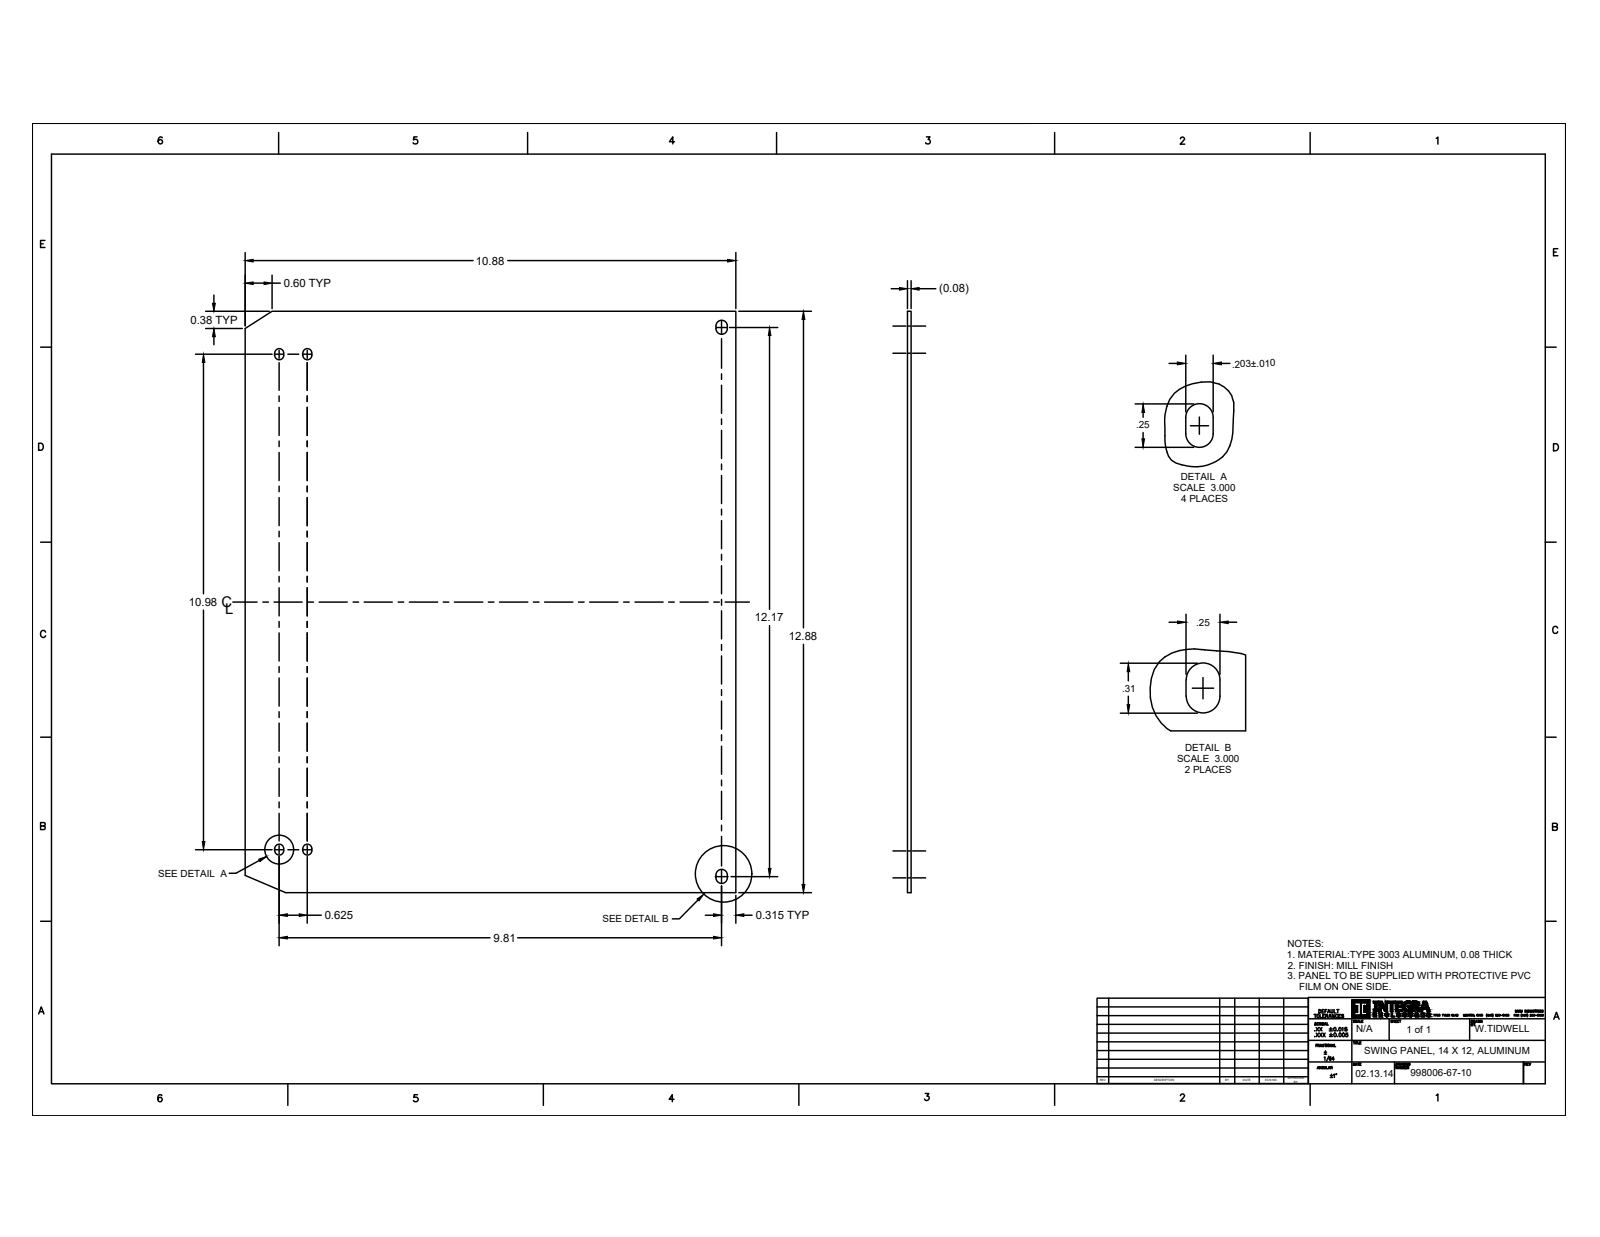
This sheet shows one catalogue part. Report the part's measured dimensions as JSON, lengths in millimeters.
{"part_name": "998006-67-10", "step_written_by": "CREO PARAMETRIC BY PTC INC, 2018050 (CONFIG_CONTROL_DESIGN)", "units": "millimeters", "bodies": {"solids": 1, "faces": 32, "planar": 20, "cylindrical": 12, "other": 0}, "overall_size": [327.2, 276.4, 2], "volume_mm3": 183000, "surface_area_mm2": 182800, "partial_cylinders_radius": [[2.6, 8], [3.2, 4]], "face_to_face_distances": [2, 276.4, 327.2, 5.2, 15.9, 4.8, 11.2, 6.4, 271.5, 265.2]}
